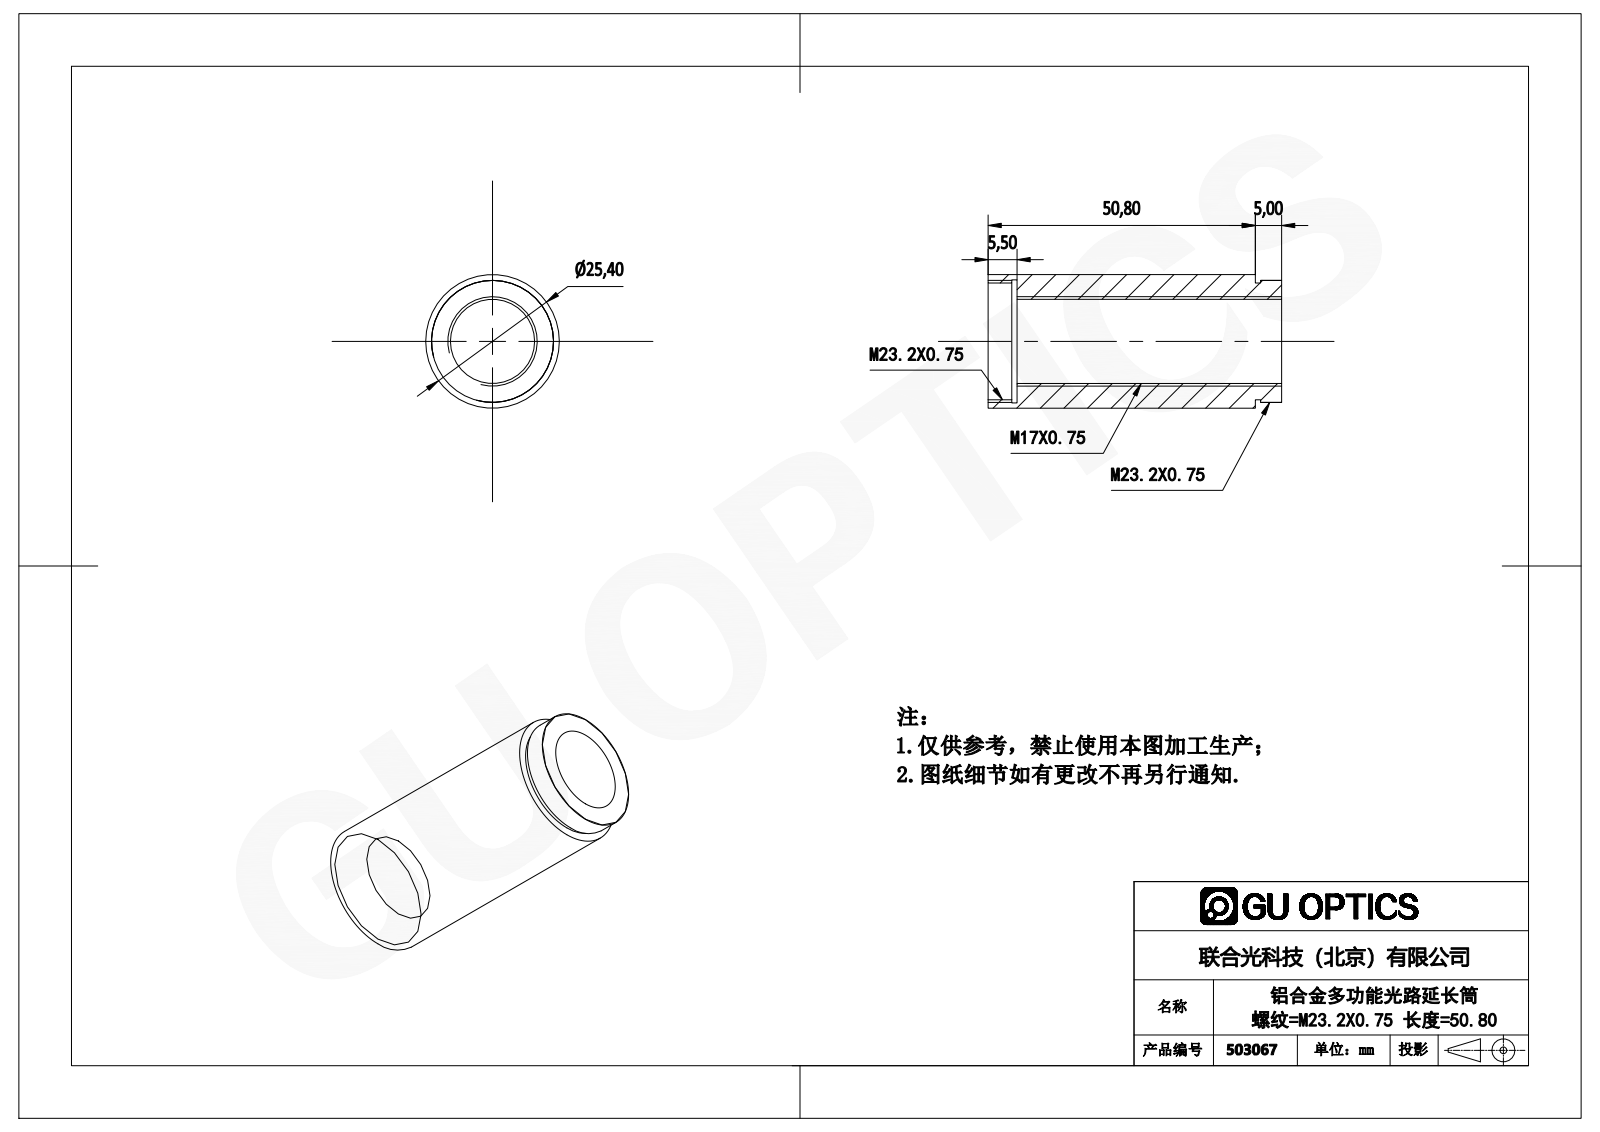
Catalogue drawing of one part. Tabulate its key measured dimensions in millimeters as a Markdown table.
| quantity | value |
| --- | --- |
| part name | 503067 |
| STEP written by | SolidWorks 2016 (AUTOMOTIVE_DESIGN) |
| units | millimeters |
| bodies | 1 solid, 18 faces (6 planar, 12 cylindrical, 0 other) |
| overall size | 55.8 × 25.4 × 25.4 |
| volume | 15 533 mm³ |
| surface area | 8 099 mm² |
| round holes (diameter × count) | 16 × 1, 22.2 × 1, 23.4 × 1 |
| round bosses / shafts (diameter × count) | 25.4 × 1, 23.2 × 1 |
| main face-to-face distances | 50.3, 45.3, 5, 5.5, 50.8, 55.8, 1, 46.3, 4.5, 51.3 |
